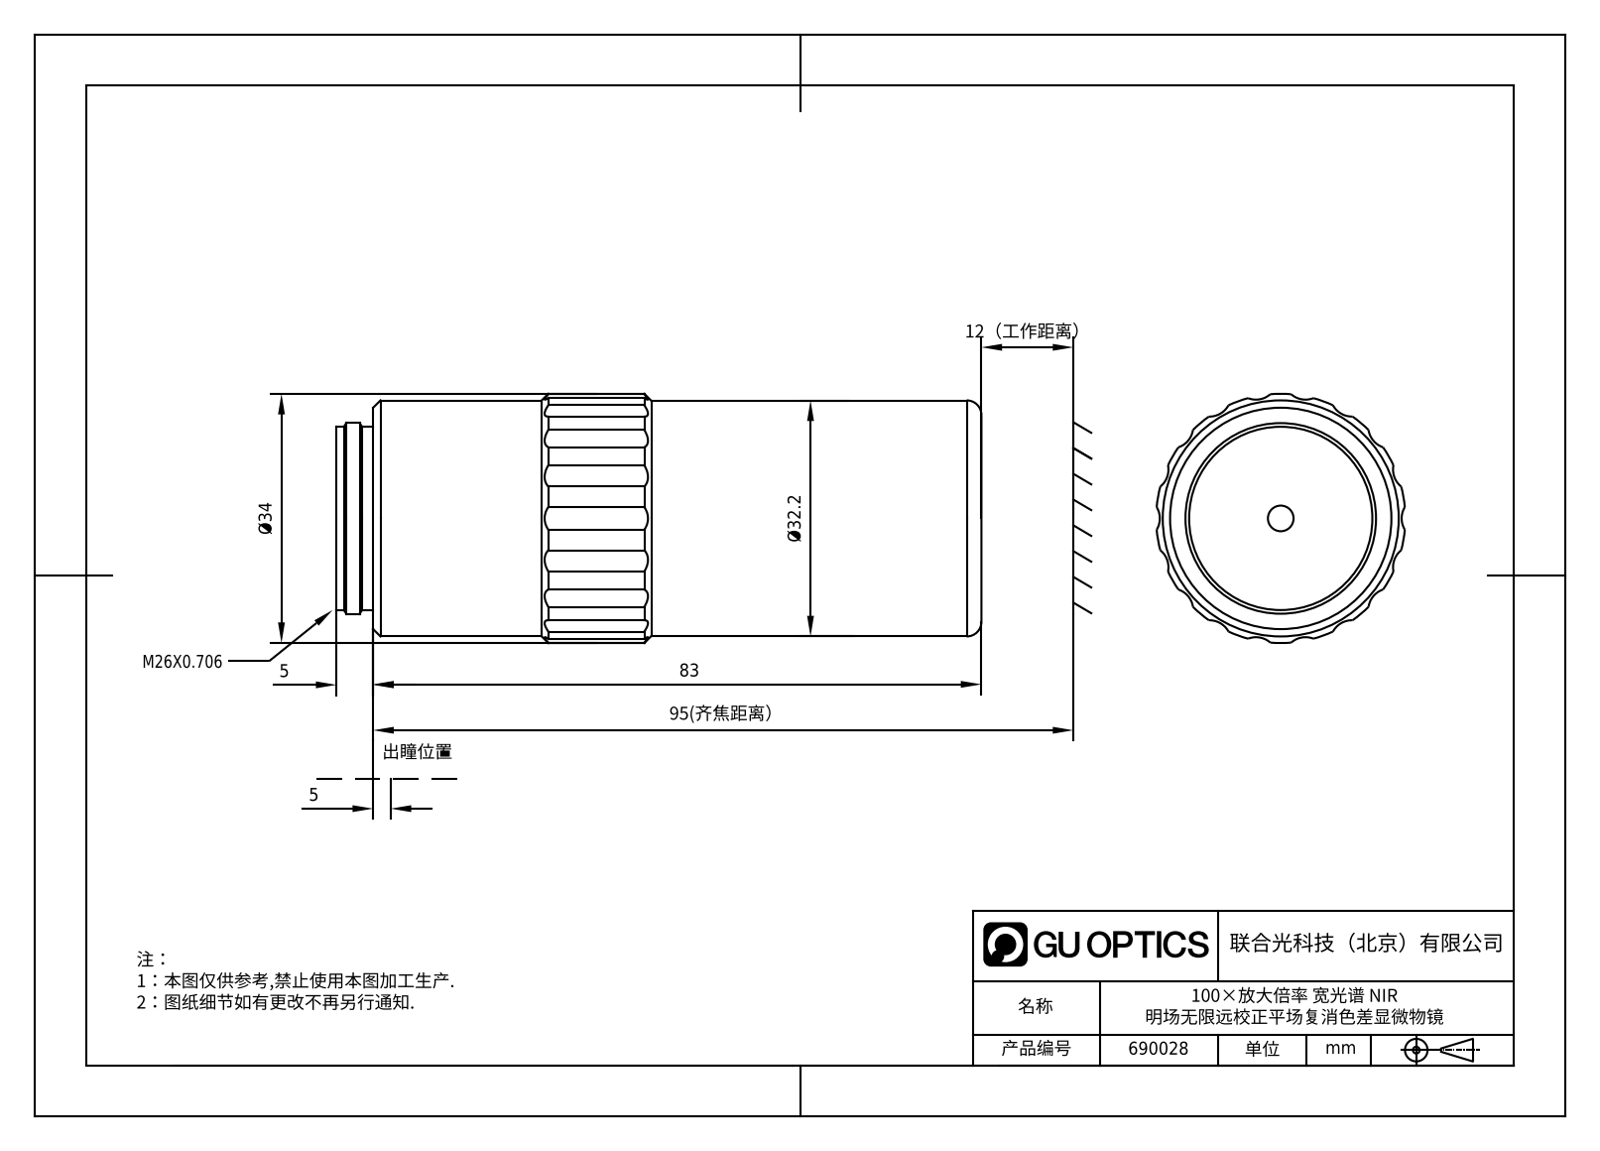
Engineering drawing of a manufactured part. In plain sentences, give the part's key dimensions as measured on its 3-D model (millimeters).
The part is named "MPA-NIR100x_378-826-15_1; 690028_1". Its 3-D file was written by "SolidWorks 2020 (CONFIG_CONTROL_DESIGN)". It is 1 solid with 55 faces: 6 planar, 43 cylindrical and 6 other. Overall it measures 88 by 34 by 33.86 millimeters. Its volume is 70 839 cubic millimeters and its surface area 10 570 square millimeters. Round holes: 1 of diameter 3.5, 1 of diameter 16. Round bosses or shafts: 1 of diameter 32.2, 1 of diameter 26, 1 of diameter 25. Partial cylindrical surfaces (rounded edges, fillets, slot ends): 18 of radius 3, 1 of radius 17. The main face-to-face distances are 88, 5, 83, 1, 87, 82, 43, 38, 44, 45.
